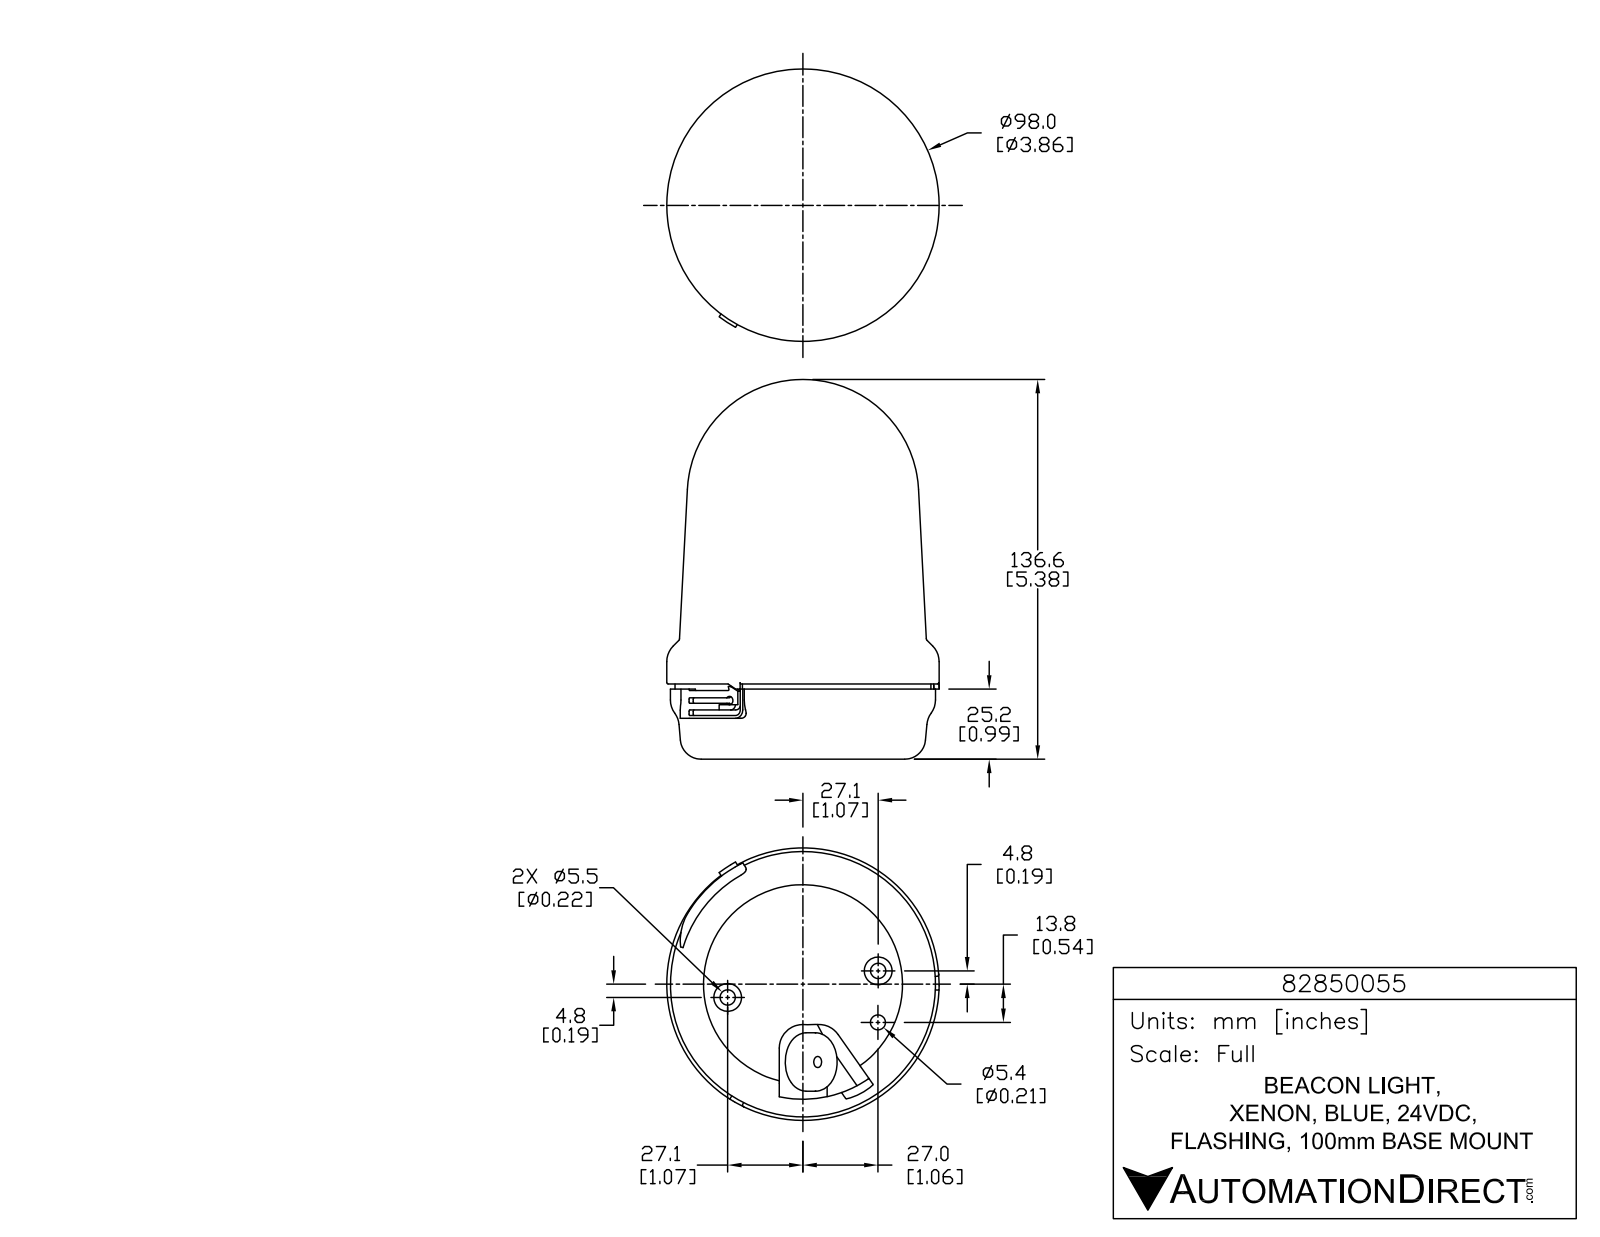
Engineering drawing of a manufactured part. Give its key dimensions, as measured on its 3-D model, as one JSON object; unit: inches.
{"part_name": "82850055", "step_written_by": "SolidWorks 2015 (AUTOMOTIVE_DESIGN)", "units": "inches", "bodies": {"solids": 1, "faces": 872, "planar": 566, "cylindrical": 204, "other": 102}, "overall_size": [5.378, 3.858, 3.858], "volume_in3": 44.69, "surface_area_in2": 73.66, "round_holes": [[0.059, 3], [0.217, 2], [0.157, 1], [0.213, 1], [2.819, 1]], "round_bosses_or_shafts": [[0.339, 3], [0.084, 3], [0.394, 2], [3.858, 1], [3.756, 1], [3.626, 1], [0.827, 1]], "partial_cylinders_radius": [[0.005, 9], [0.005, 6], [0.012, 6], [0.012, 6], [0.012, 6], [0.196, 6], [0.02, 5], [0.039, 4]], "face_to_face_distances": [1.045, 0.972, 0.073, 0.02, 0.992, 1.065, 0.236, 0.579, 0.559, 0.413], "hole_center_spacings": [1.083, 0.73, 1.193, 2.158, 2.165]}
